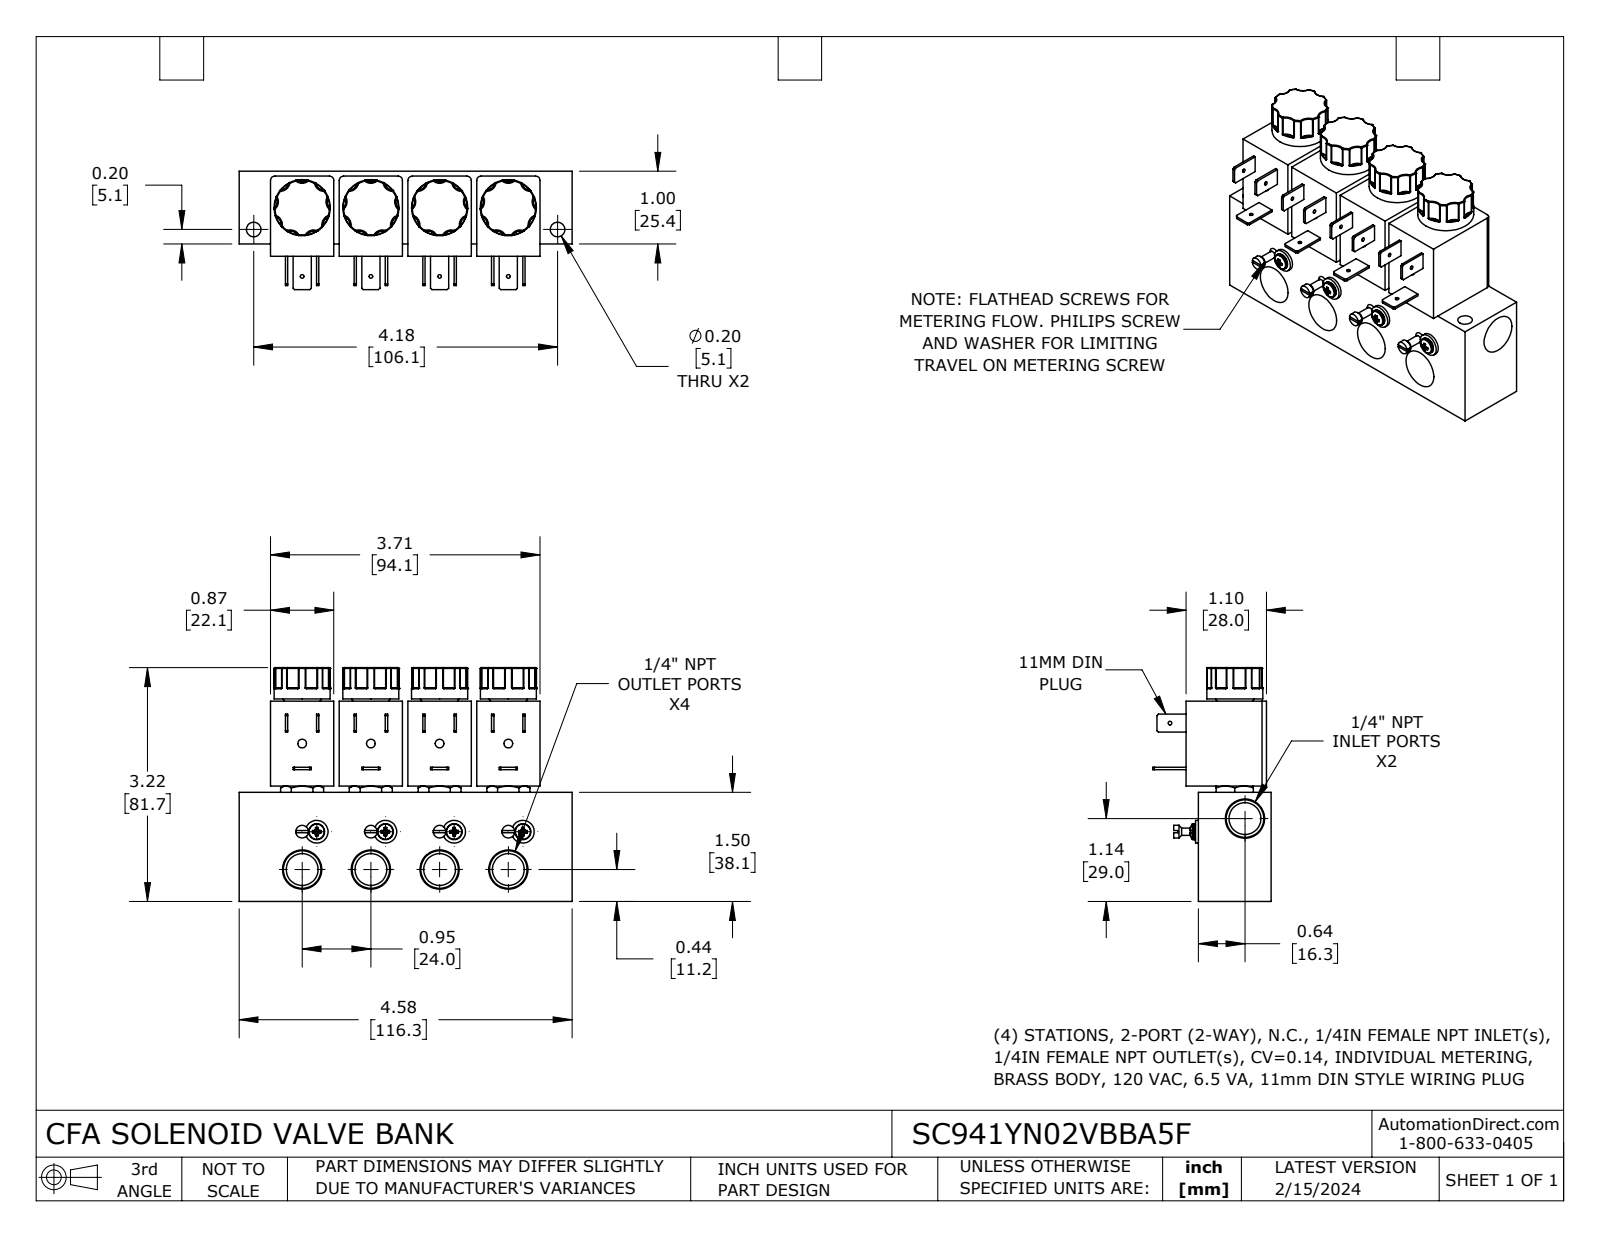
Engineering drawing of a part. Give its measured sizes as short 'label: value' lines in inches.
name: SC941YN02VBBA5F
written by: SolidWorks 2023 (CONFIG_CONTROL_DESIGN)
unit: in
bodies: 1 solid, 1098 faces (284 planar, 260 cylindrical, 554 other)
size: 4.578 × 3.215 × 1.627
volume: 11.49 in³; area: 68.21 in²
holes: 5× ⌀0.05, 5× ⌀0.438, 4× ⌀0.12, 2× ⌀0.2
bosses: 4× ⌀0.77, 4× ⌀0.312, 4× ⌀0.219, 4× ⌀0.175, 4× ⌀0.1
rounds: 72× R0.01, 28× R0.133, 8× R0.06, 8× R0.132
face distances: 1, 0.945, 1.169, 0.169, 1.89, 0.87, 1.815, 1.5, 0.065, 0.935
hole spacings: 0.945, 1.732, 1.973, 0.945, 1.89, 1.89, 2.835, 1.973
